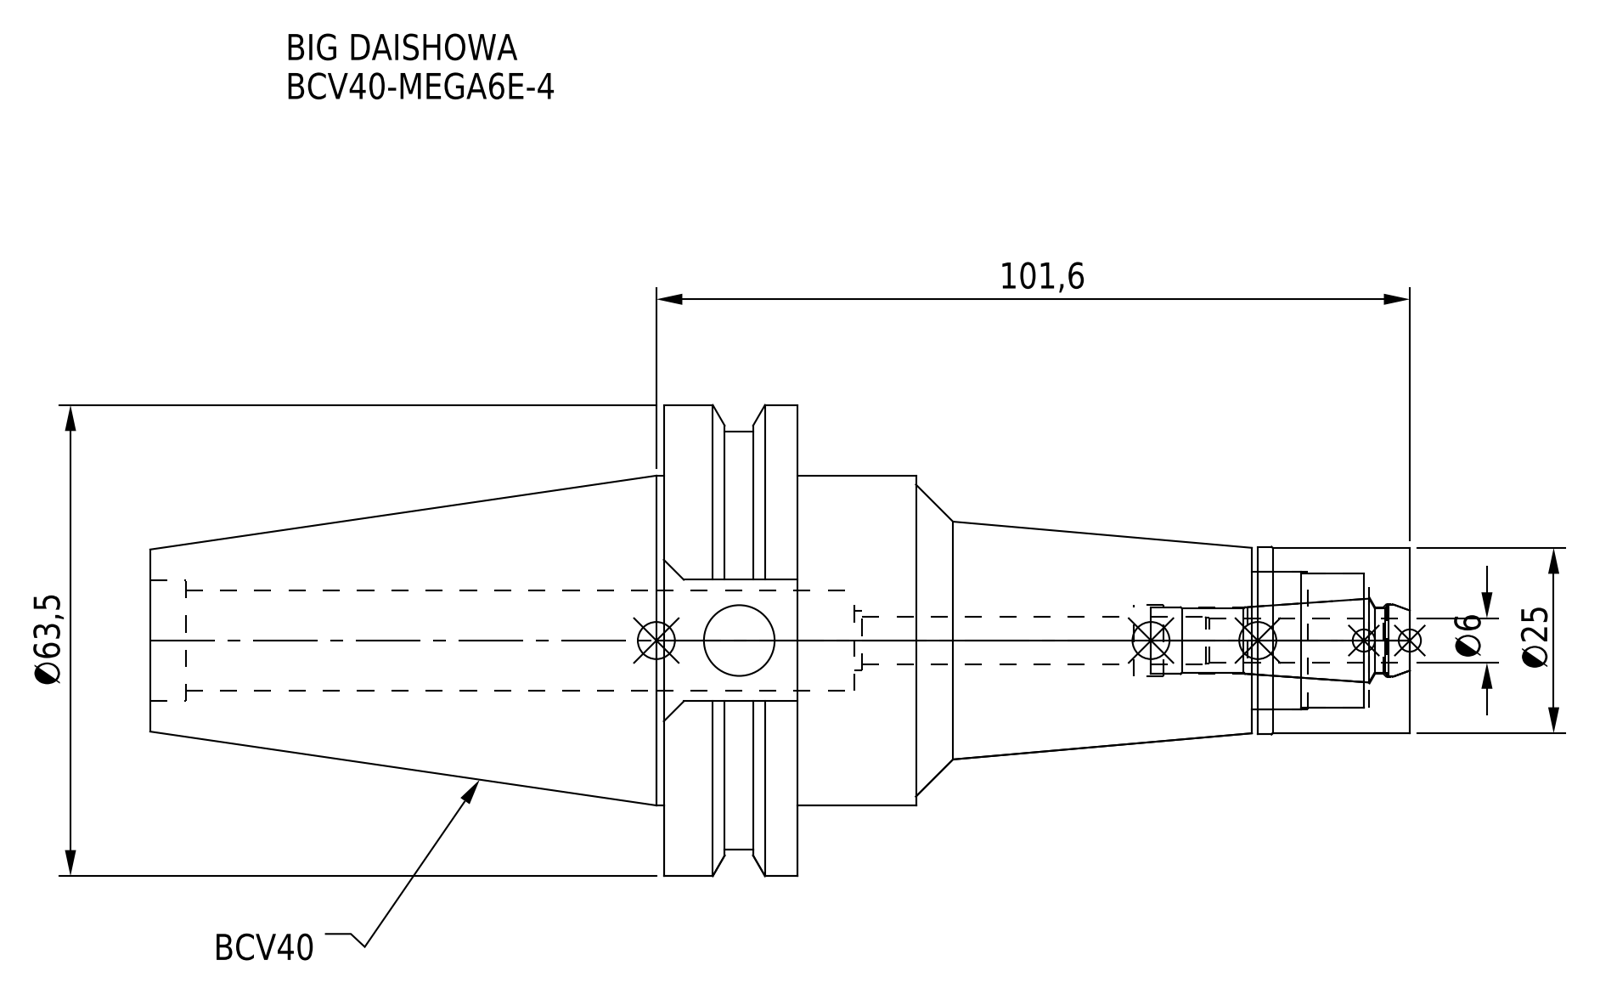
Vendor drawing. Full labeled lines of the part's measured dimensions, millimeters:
Part name (STEP PRODUCT): BCV40-MEGA6E-4-060-FreeParts; BCV40-MEGA6E-4; MEN6_1.stp; DXF_TEMP_ASSY_ASM_4_ASM.stp (+3 more)
STEP written by: SolidWorks 2019 (CONFIG_CONTROL_DESIGN)
Units: millimetres
Bodies: 2 solids, 93 faces (31 planar, 42 cylindrical, 20 other)
Overall size (bounding box): 144.45 × 63.5 × 61.35
Volume: 147 208 mm³ · Surface area: 29 966 mm²
Round holes (diameter × count): ⌀6.4 ×1, ⌀8 ×1, ⌀9 ×1, ⌀9.53 ×1, ⌀9.6 ×1, ⌀9.9 ×1, ⌀13.6 ×1, ⌀16.32 ×1, ⌀18 ×1, ⌀18.5 ×1
Round bosses / shafts (diameter × count): ⌀63.5 ×1, ⌀56.36 ×1, ⌀44.45 ×1, ⌀25.3 ×1, ⌀25 ×1
Main face-to-face distances: 18.05, 15.95, 34, 41.2, 57.15, 75.2, 144.45, 103.25, 87.3, 69.25
